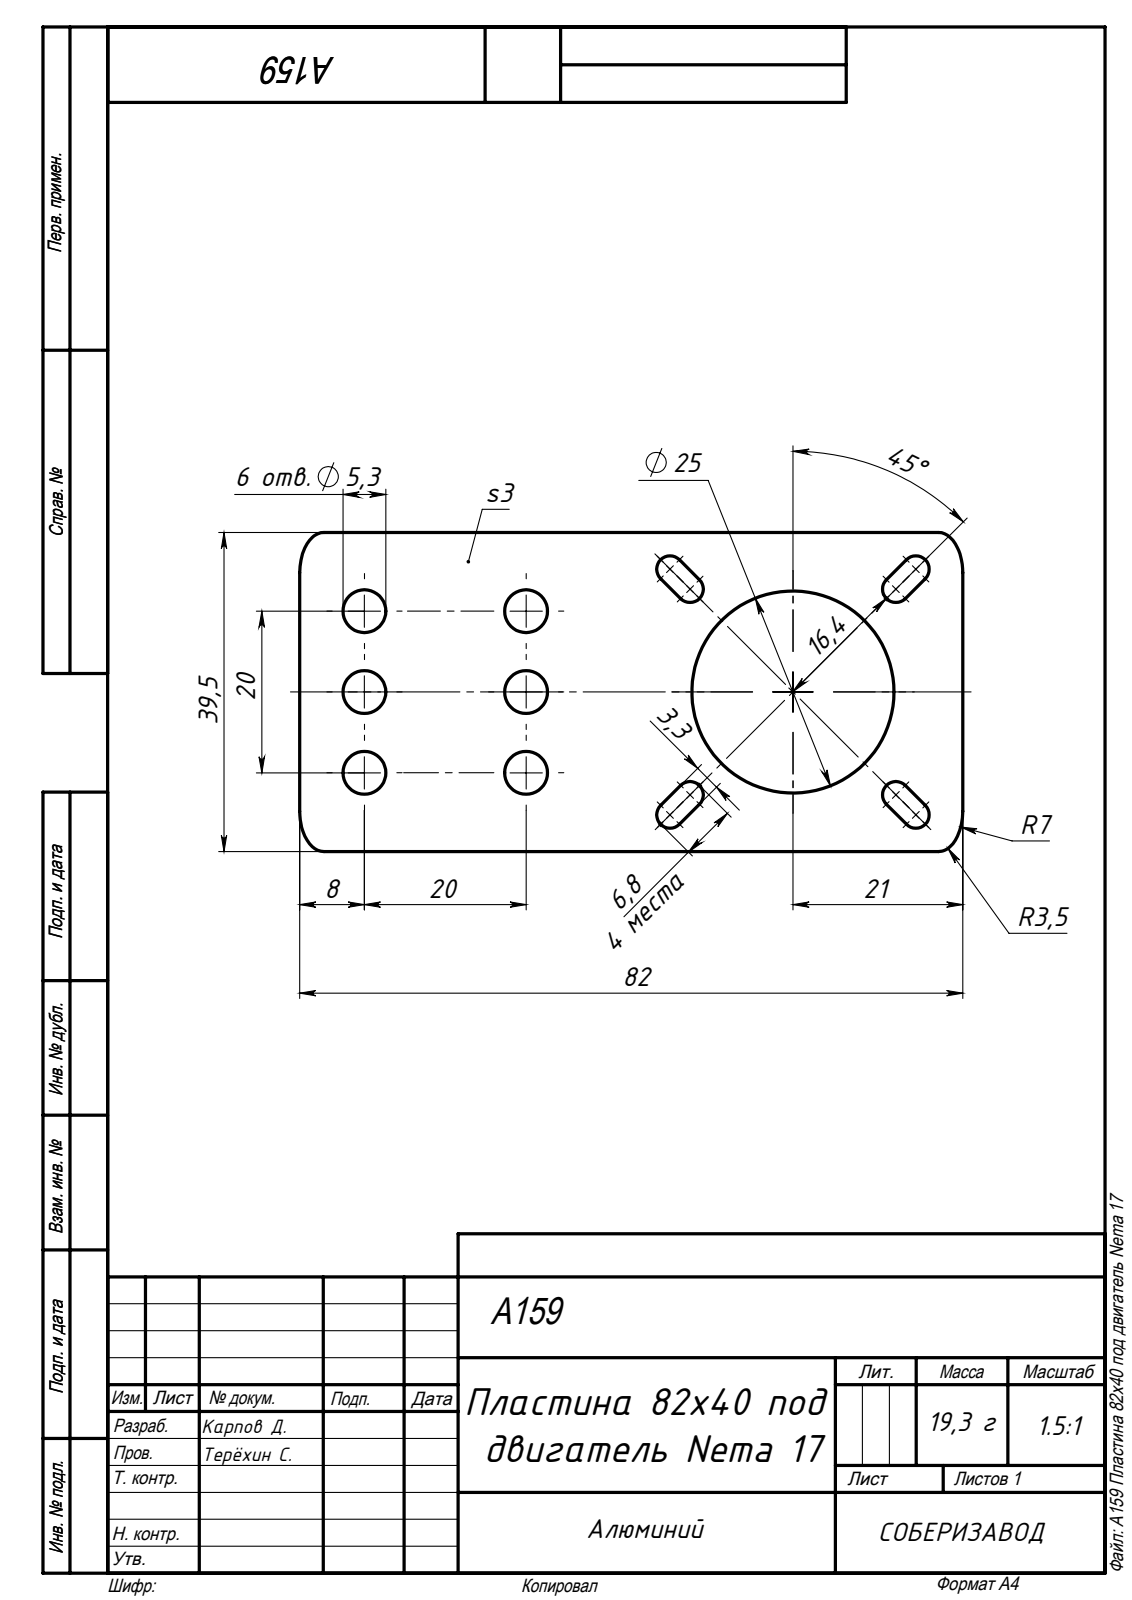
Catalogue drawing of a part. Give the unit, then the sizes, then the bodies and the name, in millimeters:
Units: millimetres
Overall size (bounding box): 82 × 39.5 × 3
Round holes (diameter × count): ⌀5.3 ×6, ⌀25 ×1
Partial cylindrical surfaces — rounded edges, fillets, slot ends (radius × count): R1.65 ×8
Main face-to-face distances: 3, 39.5, 82, 3.3
Hole centre spacings: 20, 10, 22.36, 28.28, 34.48, 53.94, 33, 53
Volume: 7 568 mm³ · Surface area: 6 499 mm²
Bodies: 1 solid, 44 faces (14 planar, 26 cylindrical, 4 other)
Part name (STEP PRODUCT): A159 Пластина 82x40 под двигатель Nema 17
STEP written by: SolidWorks 2018 (AUTOMOTIVE_DESIGN)
